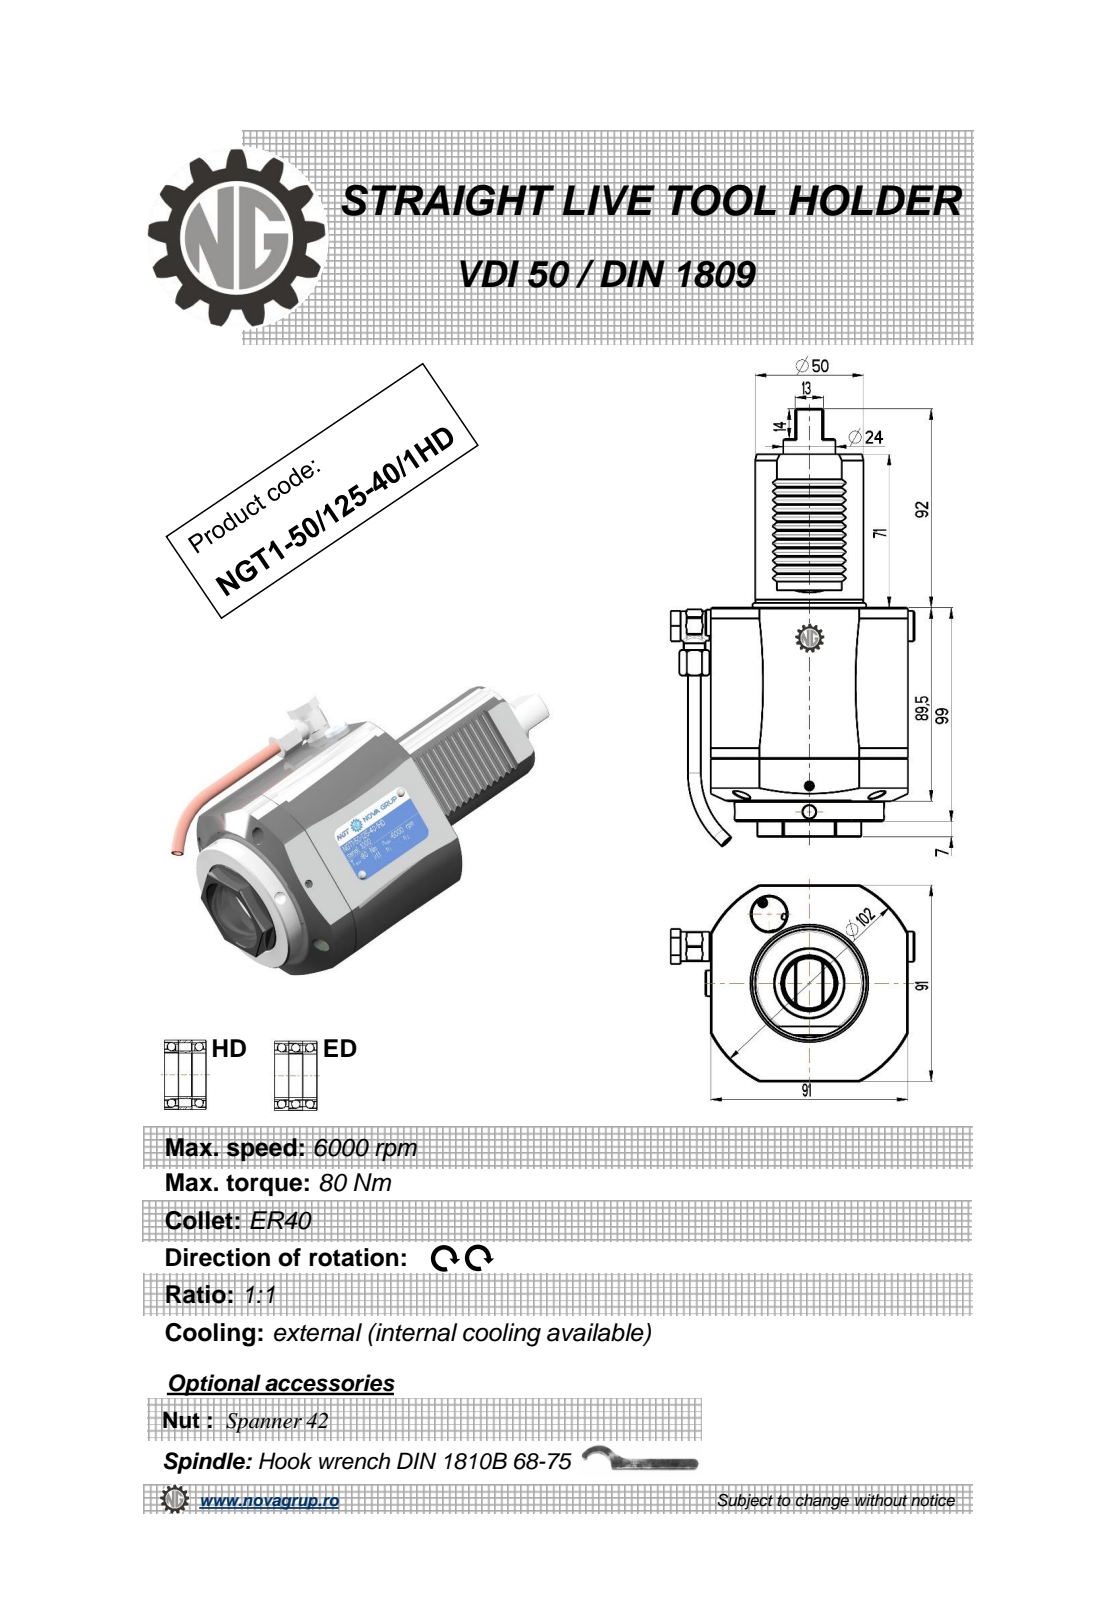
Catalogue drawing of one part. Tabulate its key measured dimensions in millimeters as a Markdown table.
| quantity | value |
| --- | --- |
| part name | NGT1_50_125_40_3HD |
| STEP written by | PRO/ENGINEER BY PARAMETRIC TECHNOLOGY CORPORATION, 2010280 (CONFIG_CONTROL_DESIGN) |
| units | millimeters |
| bodies | 1 solid, 363 faces (149 planar, 102 cylindrical, 112 other) |
| overall size | 202.44 × 112.4 × 91 |
| volume | 830 326 mm³ |
| surface area | 66 673 mm² |
| round holes (diameter × count) | 4 × 3, 6 × 2, 3 × 1, 6.2 × 1, 9 × 1, 10 × 1, 11 × 1, 36.2 × 1, 42 × 1 |
| round bosses / shafts (diameter × count) | 6 × 2, 69 × 1, 50 × 1, 24 × 1, 14 × 1, 13.6 × 1, 13 × 1, 12 × 1 |
| partial cylindrical surfaces (radius × count) | 0.3 × 12, 0.41 × 6, 0.5 × 4, 0.8 × 2, 6.25 × 1, 7.7 × 1, 24 × 1, 51 × 1 |
| main face-to-face distances | 91, 89.5, 9.5, 99, 170, 160.5, 71, 2.83, 14.14, 11.31 |
| hole center spacings | 0.4, 55.66, 56.04, 87.66 |
